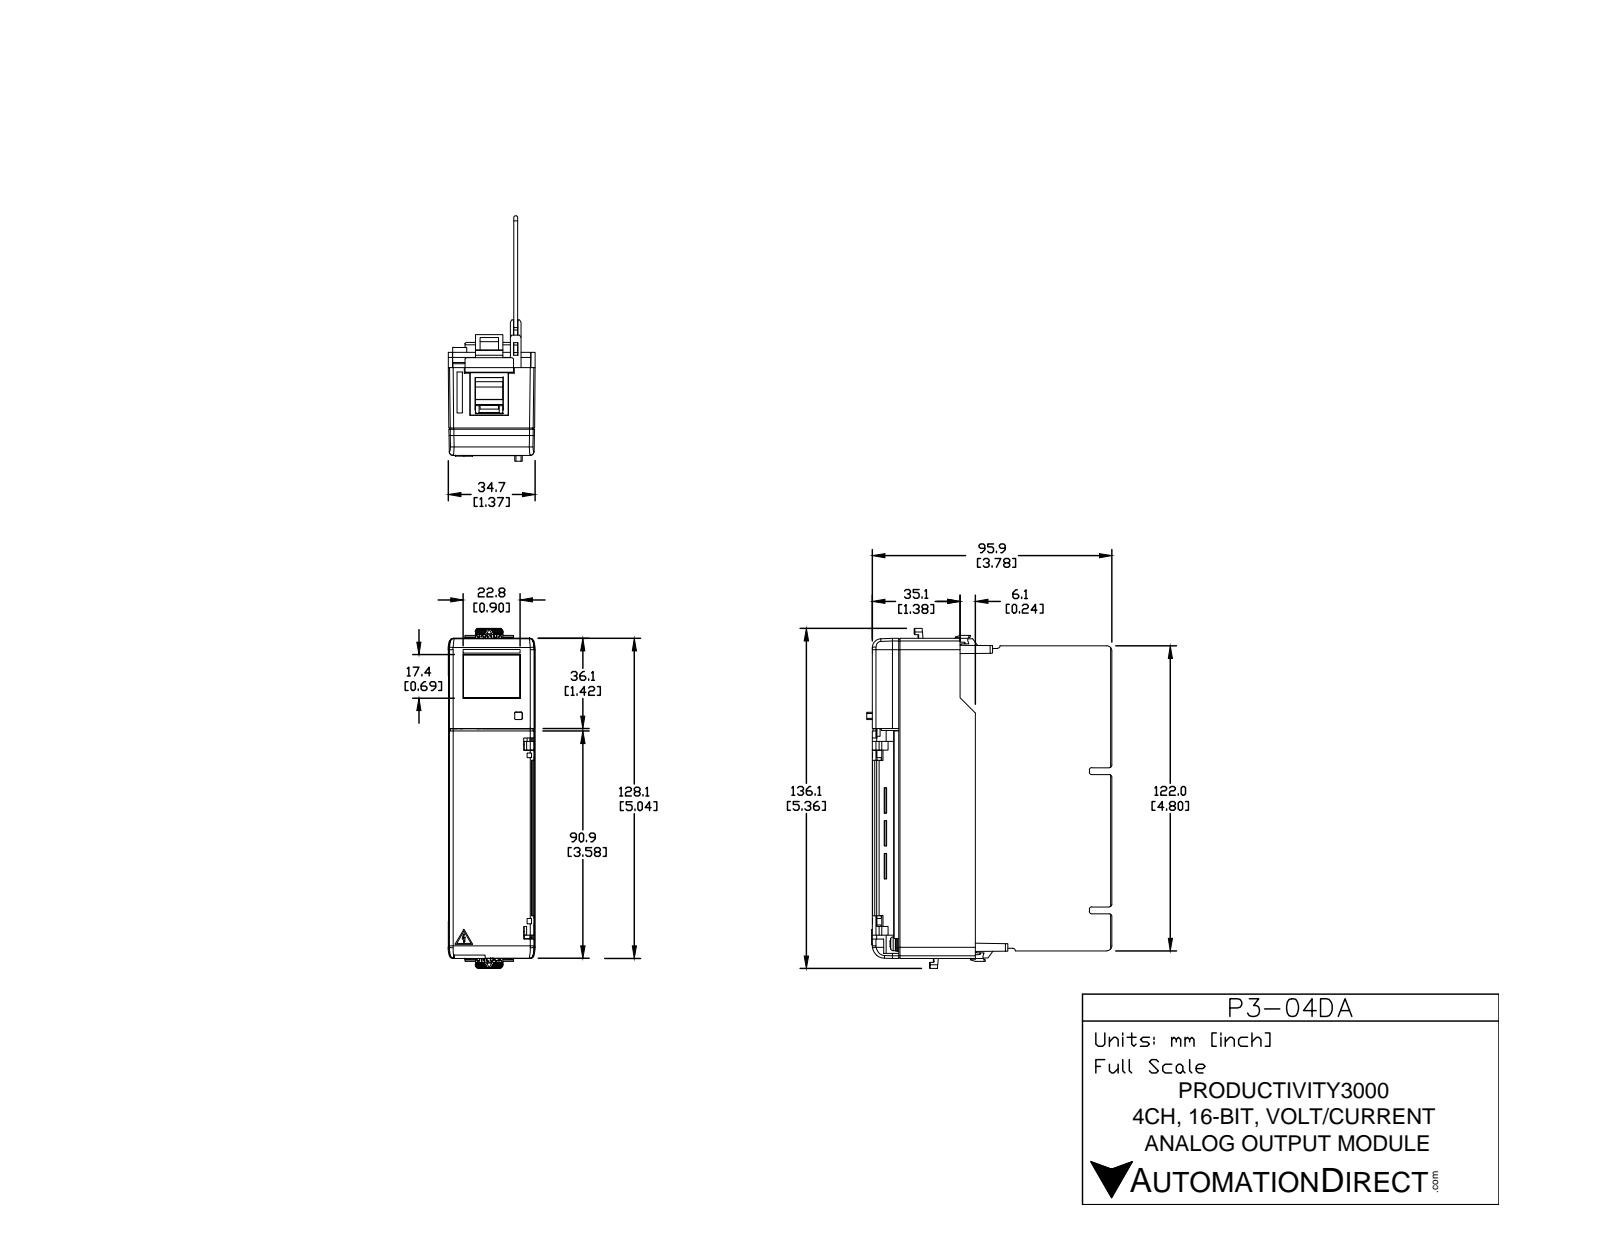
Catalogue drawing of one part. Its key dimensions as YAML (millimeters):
part_name: "P3-04DA"
step_written_by: "SolidWorks 2009 (CONFIG_CONTROL_DESIGN)"
units: millimeters
bodies: {solids: 1, faces: 3823, planar: 2833, cylindrical: 744, other: 246}
overall_size: [136.08, 98.18, 34.8]
volume: 101360
surface_area: 75361
round_holes:
  - {diameter: 3.2, count: 22}
  - {diameter: 5, count: 2}
  - {diameter: 1.8, count: 1}
round_bosses_or_shafts:
  - {diameter: 5.5, count: 22}
  - {diameter: 3, count: 22}
  - {diameter: 2.4, count: 20}
  - {diameter: 5.6, count: 2}
  - {diameter: 2.2, count: 2}
  - {diameter: 2, count: 2}
  - {diameter: 1.5, count: 1}
partial_cylinders:
  - {radius: 0.5, count: 95}
  - {radius: 1, count: 33}
  - {radius: 0.3, count: 29}
  - {radius: 1.67, count: 22}
  - {radius: 1.5, count: 13}
  - {radius: 2, count: 6}
  - {radius: 0.2, count: 5}
  - {radius: 0.1, count: 4}
face_to_face_distances: [1.6, 1.7, 28.23, 26.53, 32.56, 22.2, 2.2, 7.9, 6.8, 5.32]
hole_center_spacings: [8.68, 7.62, 13.84, 15.24, 20.59, 22.86, 27.79, 30.48]
